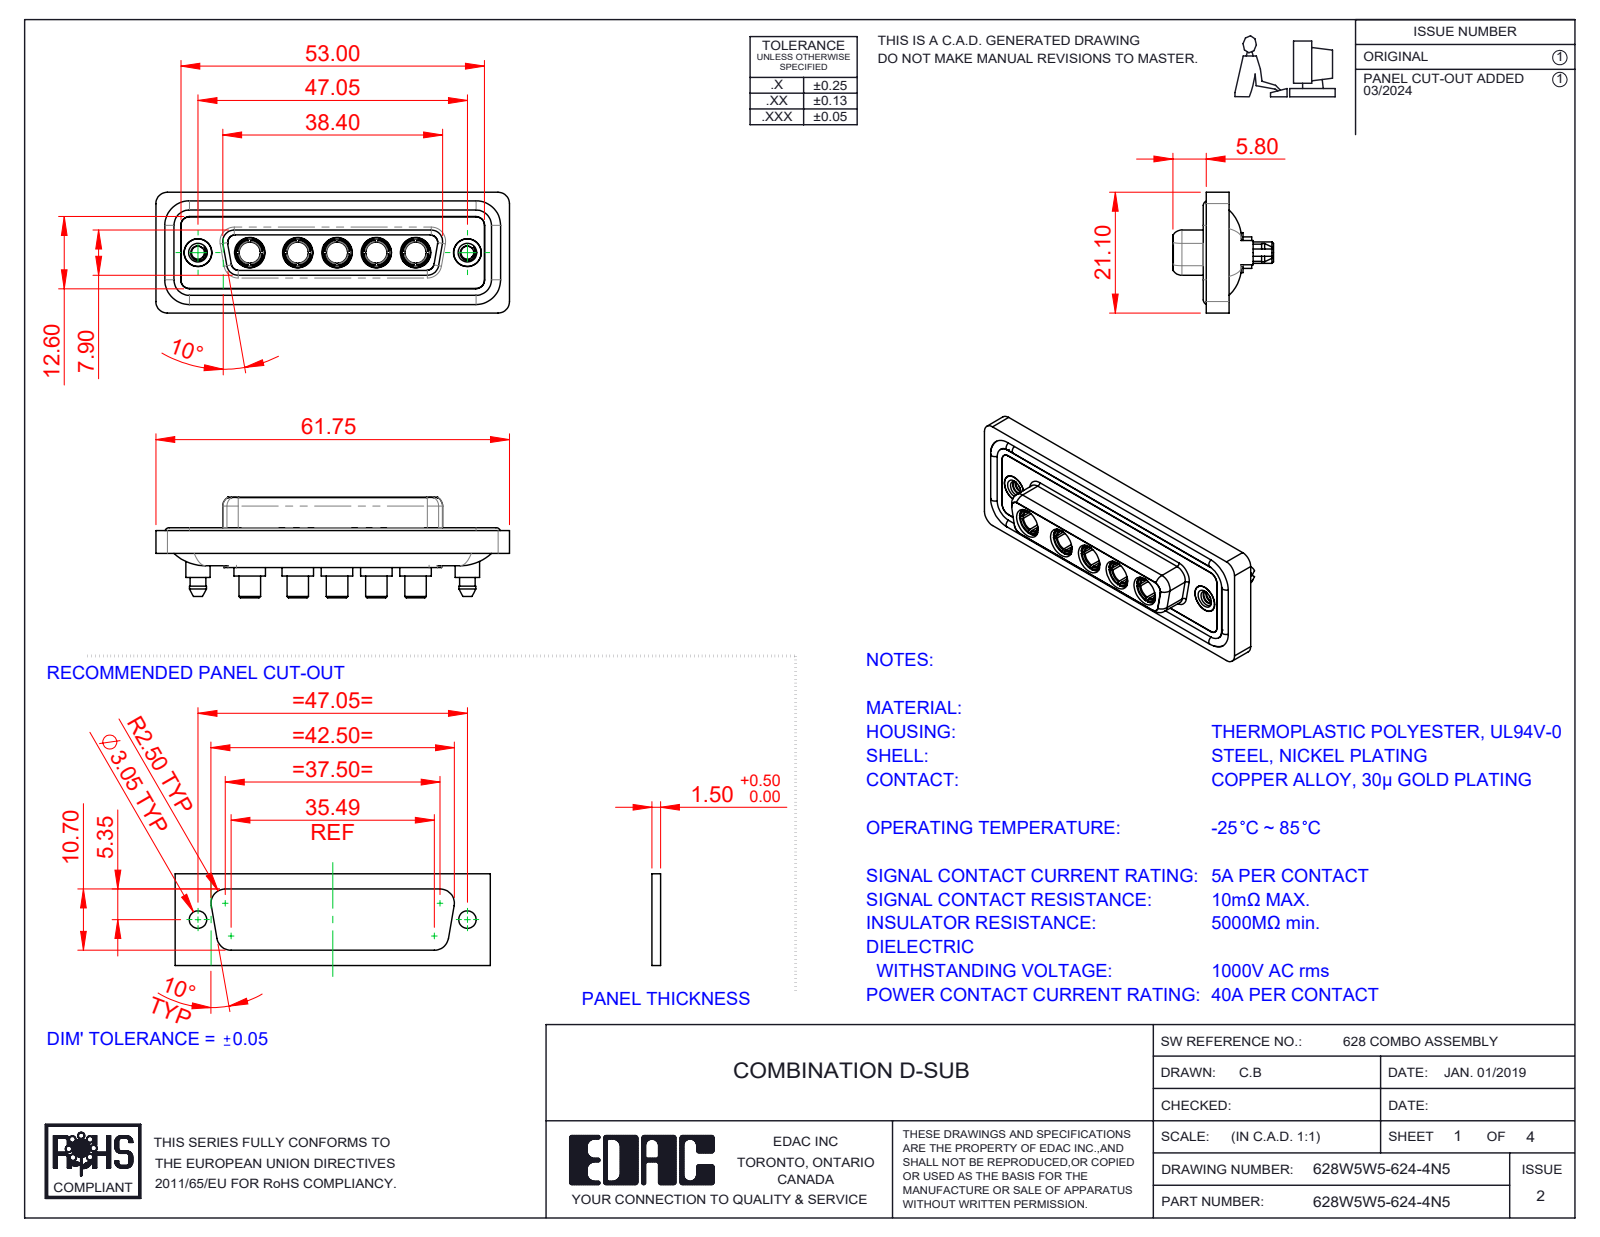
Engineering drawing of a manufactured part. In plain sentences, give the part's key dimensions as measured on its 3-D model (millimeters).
The part is named "628Combo Shell Front_25 Contacts; 628Combo Threaded Boardlock_5; 628Combo Housing_5W5; Power Socket_40A S (+3 more)". Its 3-D file was written by "SolidWorks 2023 (CONFIG_CONTROL_DESIGN)". It is 17 solids with 806 faces: 266 planar, 335 cylindrical and 205 other. Overall it measures 61.75 by 21.1 by 17.55 millimeters. Its volume is 8 399 cubic millimeters and its surface area 13 803 square millimeters. Round holes: 7 of diameter 4.85, 5 of diameter 3.7, 5 of diameter 5.3, 2 of diameter 2.26, 2 of diameter 4, 2 of diameter 4.05, 2 of diameter 5. Round bosses or shafts: 5 of diameter 5.5, 5 of diameter 5.2, 5 of diameter 4.96, 5 of diameter 4.75, 5 of diameter 3.75, 4 of diameter 1.6, 2 of diameter 5.4, 2 of diameter 4.95. Partial cylindrical surfaces (rounded edges, fillets, slot ends): 24 of radius 1.5, 18 of radius 2, 10 of radius 1.6, 8 of radius 1.35, 5 of radius 2.1, 4 of radius 0.25, 4 of radius 0.5, 4 of radius 0.6. The main face-to-face distances are 0.4, 1.8, 7.45, 5.65, 0.5, 7.05, 6.6, 1.6, 1.1, 2.9. The hole center spacings are 6.86, 9.04, 13.72, 38.01, 8.39, 15.25, 15.9, 17.43.
